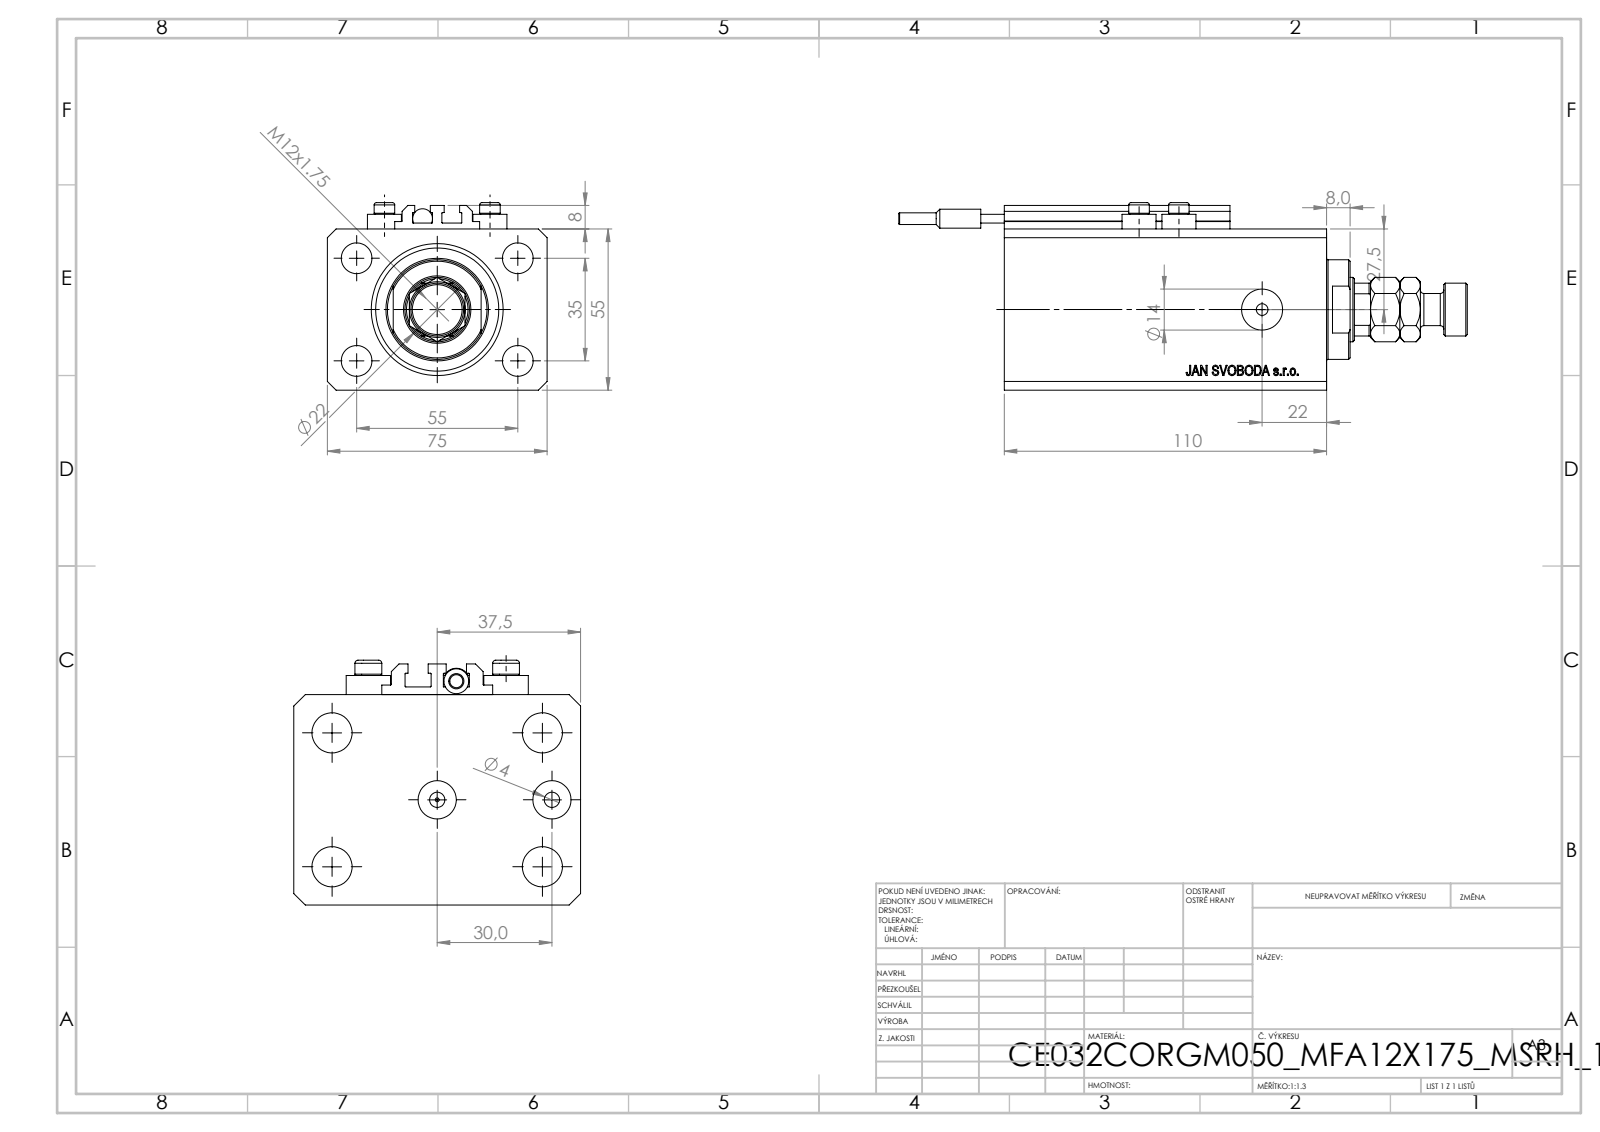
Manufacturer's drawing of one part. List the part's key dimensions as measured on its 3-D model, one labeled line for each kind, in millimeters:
Part name (STEP PRODUCT): ALLEN BOLT V250CE; V250CE_C_VCP; V250CE_VC_C; V250CE_C_Body (+2 more)
STEP written by: SolidWorks 2019 (CONFIG_CONTROL_DESIGN)
Units: millimetres
Bodies: 10 solids, 1116 faces (536 planar, 98 cylindrical, 482 other)
Overall size (bounding box): 194 × 75 × 64
Volume: 418 301 mm³ · Surface area: 95 680 mm²
Round holes (diameter × count): ⌀4 ×8, ⌀10.5 ×5, ⌀10 ×2, ⌀14 ×2, ⌀1.25 ×1, ⌀22 ×1, ⌀32 ×1, ⌀45 ×1
Round bosses / shafts (diameter × count): ⌀11.6 ×4, ⌀7 ×4, ⌀34 ×1, ⌀18 ×1, ⌀11 ×1, ⌀6.8 ×1, ⌀6.5 ×1, ⌀4 ×1
Partial cylindrical surfaces — rounded edges, fillets, slot ends (radius × count): R0.2 ×10, R10.5 ×1
Main face-to-face distances: 55, 75, 110, 15, 95, 9.9, 85.1, 100.1, 8, 2.5
Hole centre spacings: 32.6, 13.6, 17.68, 35, 36, 38.48, 55, 60.1
